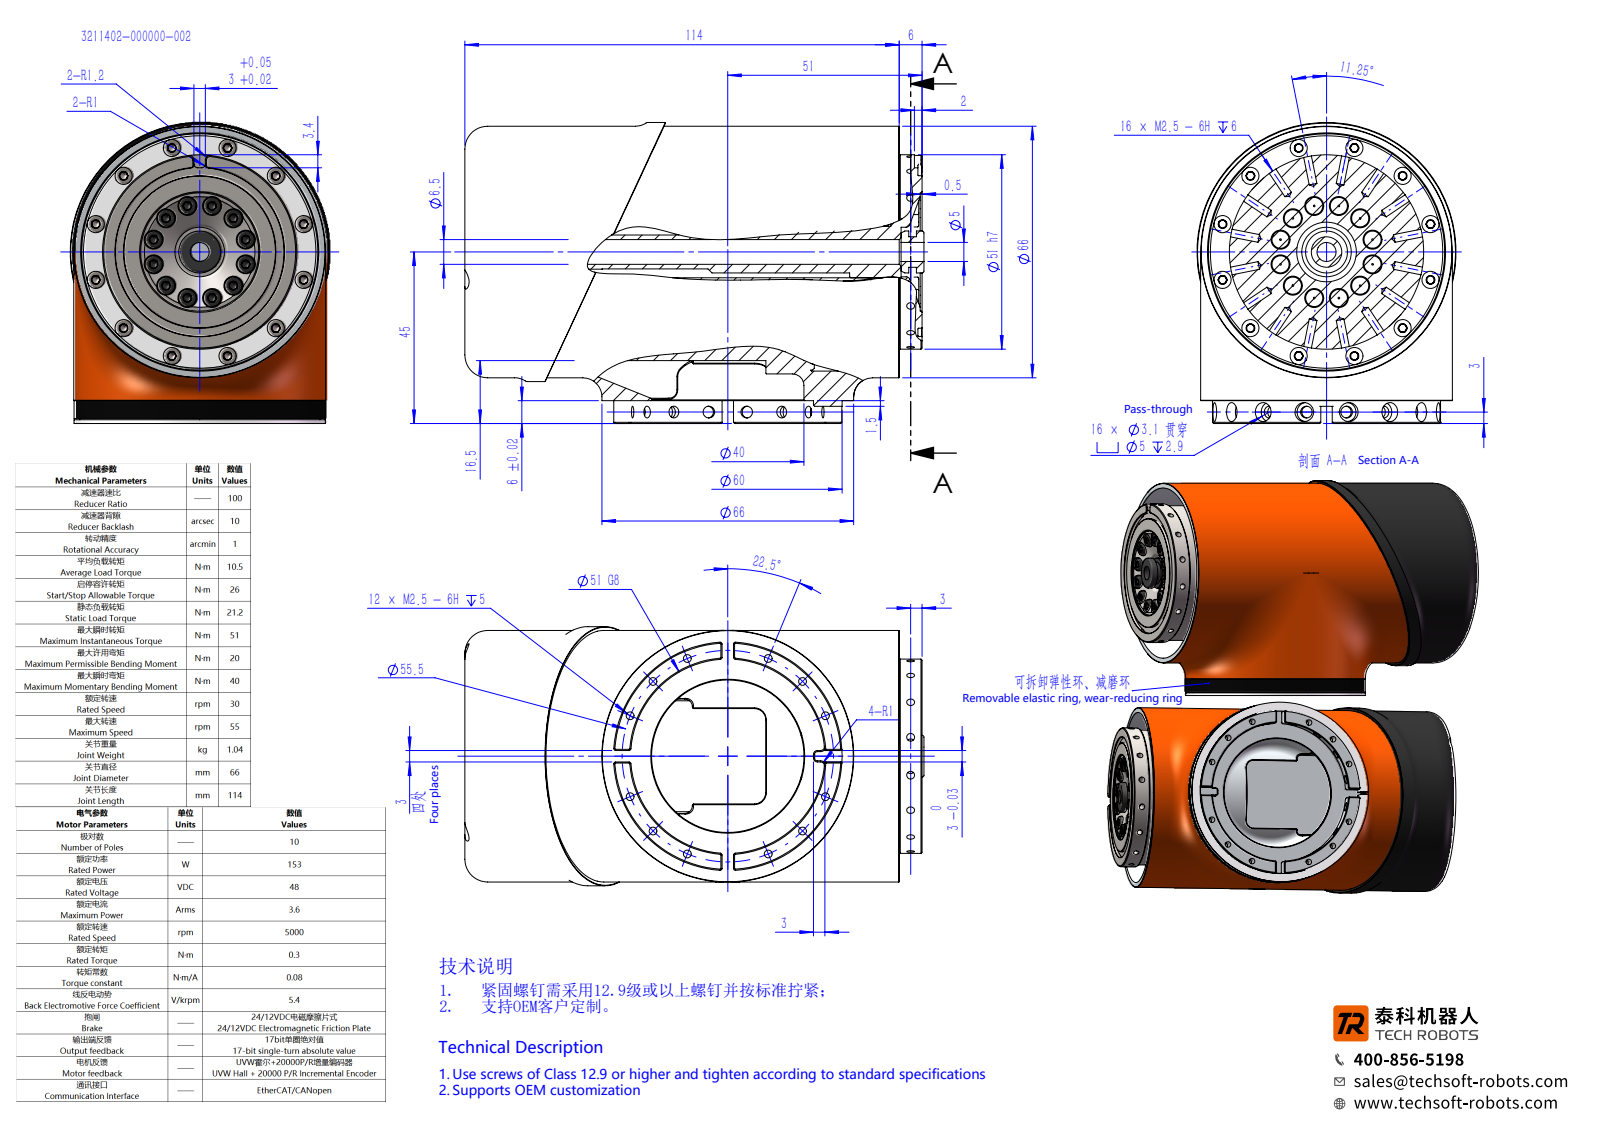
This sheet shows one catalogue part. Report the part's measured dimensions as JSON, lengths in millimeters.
{"step_written_by": "SolidWorks 2016 (CONFIG_CONTROL_DESIGN)", "units": "millimeters", "bodies": {"solids": 27, "faces": 1508, "planar": 493, "cylindrical": 459, "other": 556}, "overall_size": [120.52, 79, 68], "volume_mm3": 391852, "surface_area_mm2": 68387, "round_holes": [[2.05, 52], [5, 32], [2.9, 27], [3.1, 16], [40, 2], [6.5, 1], [13, 1], [13.5, 1], [21, 1], [31, 1], [44.3, 1], [51, 1]], "round_bosses_or_shafts": [[4.5, 24], [2.38, 24], [68, 1], [66.1, 1], [66, 1], [62, 1], [60, 1], [51, 1]], "partial_cylinders_radius": [[0.5, 12], [1, 8], [0.3, 4], [3, 4], [1.2, 2], [2, 2], [31.5, 1], [32, 1]], "face_to_face_distances": [114.02, 6, 10.5, 22.3, 91.72, 120.02, 28.3, 16.5, 114.82, 23.1], "hole_center_spacings": [36.16, 12.5, 18.51, 24.52, 28.25, 30.9, 39.58, 15.75]}
